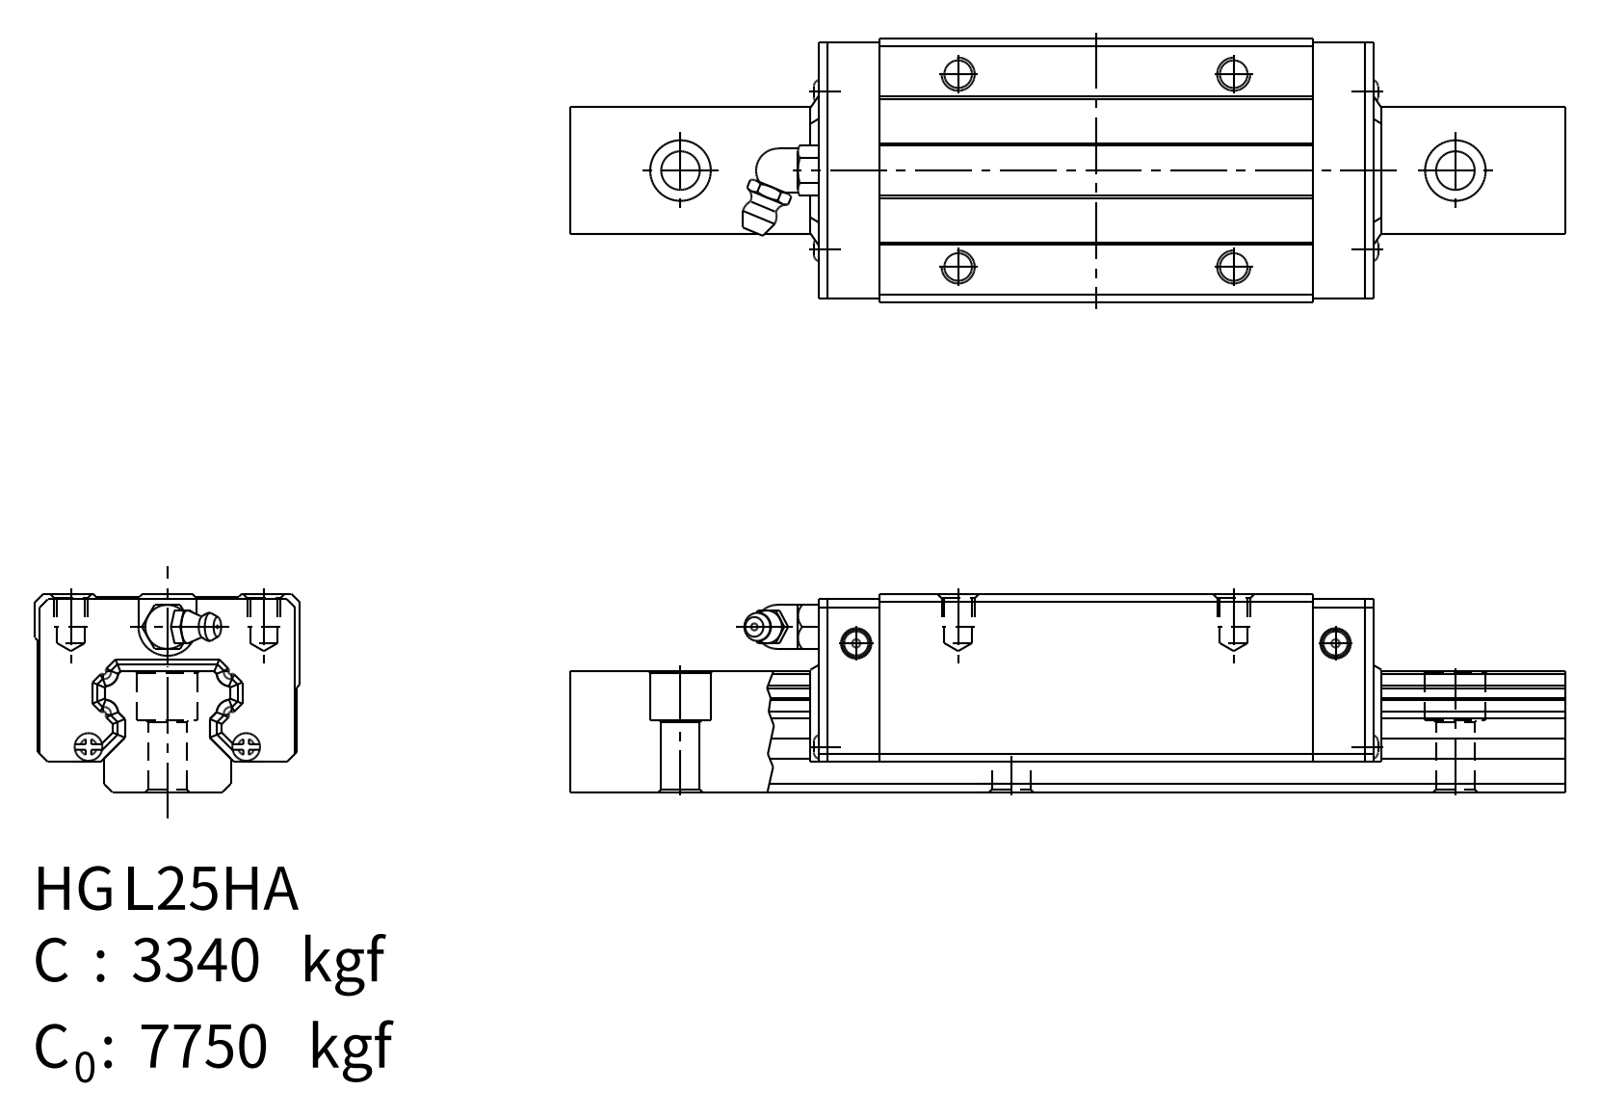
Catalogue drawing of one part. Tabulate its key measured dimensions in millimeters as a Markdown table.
| quantity | value |
| --- | --- |
| part name | PRT0001; PRT0002; ASM_HG25-H_ASM_6_ASM_ASM_ASM; HG25H_ASM_ASM_ASM (+2 more) |
| STEP written by | PRO/ENGINEER BY PARAMETRIC TECHNOLOGY CORPORATION, 2004360 (CONFIG_CONTROL_DESIGN) |
| units | millimeters |
| bodies | 2 solids, 1180 faces (1024 planar, 148 cylindrical, 8 other) |
| overall size | 140 × 48 × 36 |
| volume | 173 892 mm³ |
| surface area | 36 708 mm² |
| round holes (diameter × count) | 6 × 4, 5 × 2 |
| partial cylindrical surfaces (radius × count) | 0.12 × 68, 0.18 × 12, 0.24 × 4, 1.75 × 4 |
| main face-to-face distances | 35.5, 0.5, 22, 5.5, 16.5, 35, 36, 30.5, 14, 3.7 |
| hole center spacings | 35, 50, 61.03, 90.6 |
